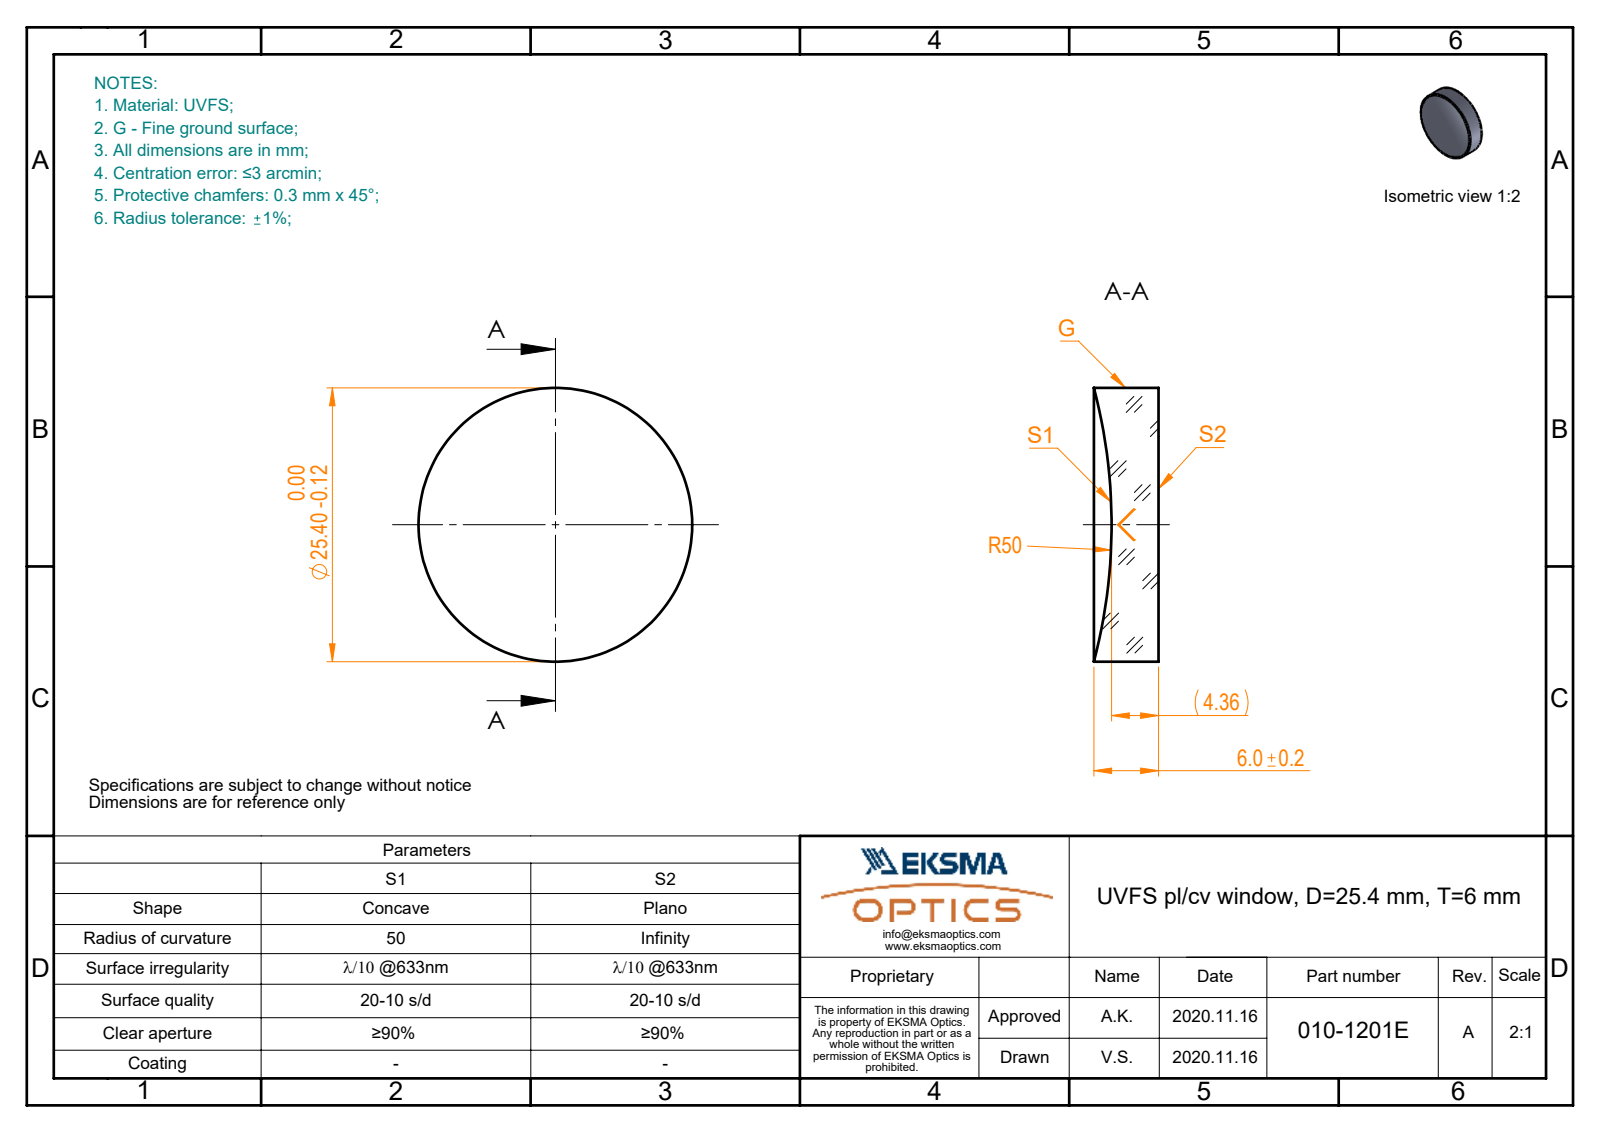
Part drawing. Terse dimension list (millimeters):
name: 010-1201E_UVFS_PCV_window
written by: SolidWorks 2019 (CONFIG_CONTROL_DESIGN)
unit: mm
bodies: 1 solid, 5 faces (1 planar, 2 cylindrical, 2 other)
size: 25.4 × 25.4 × 6
volume: 2 622 mm³; area: 1 501 mm²
bosses: 1× ⌀25.4
